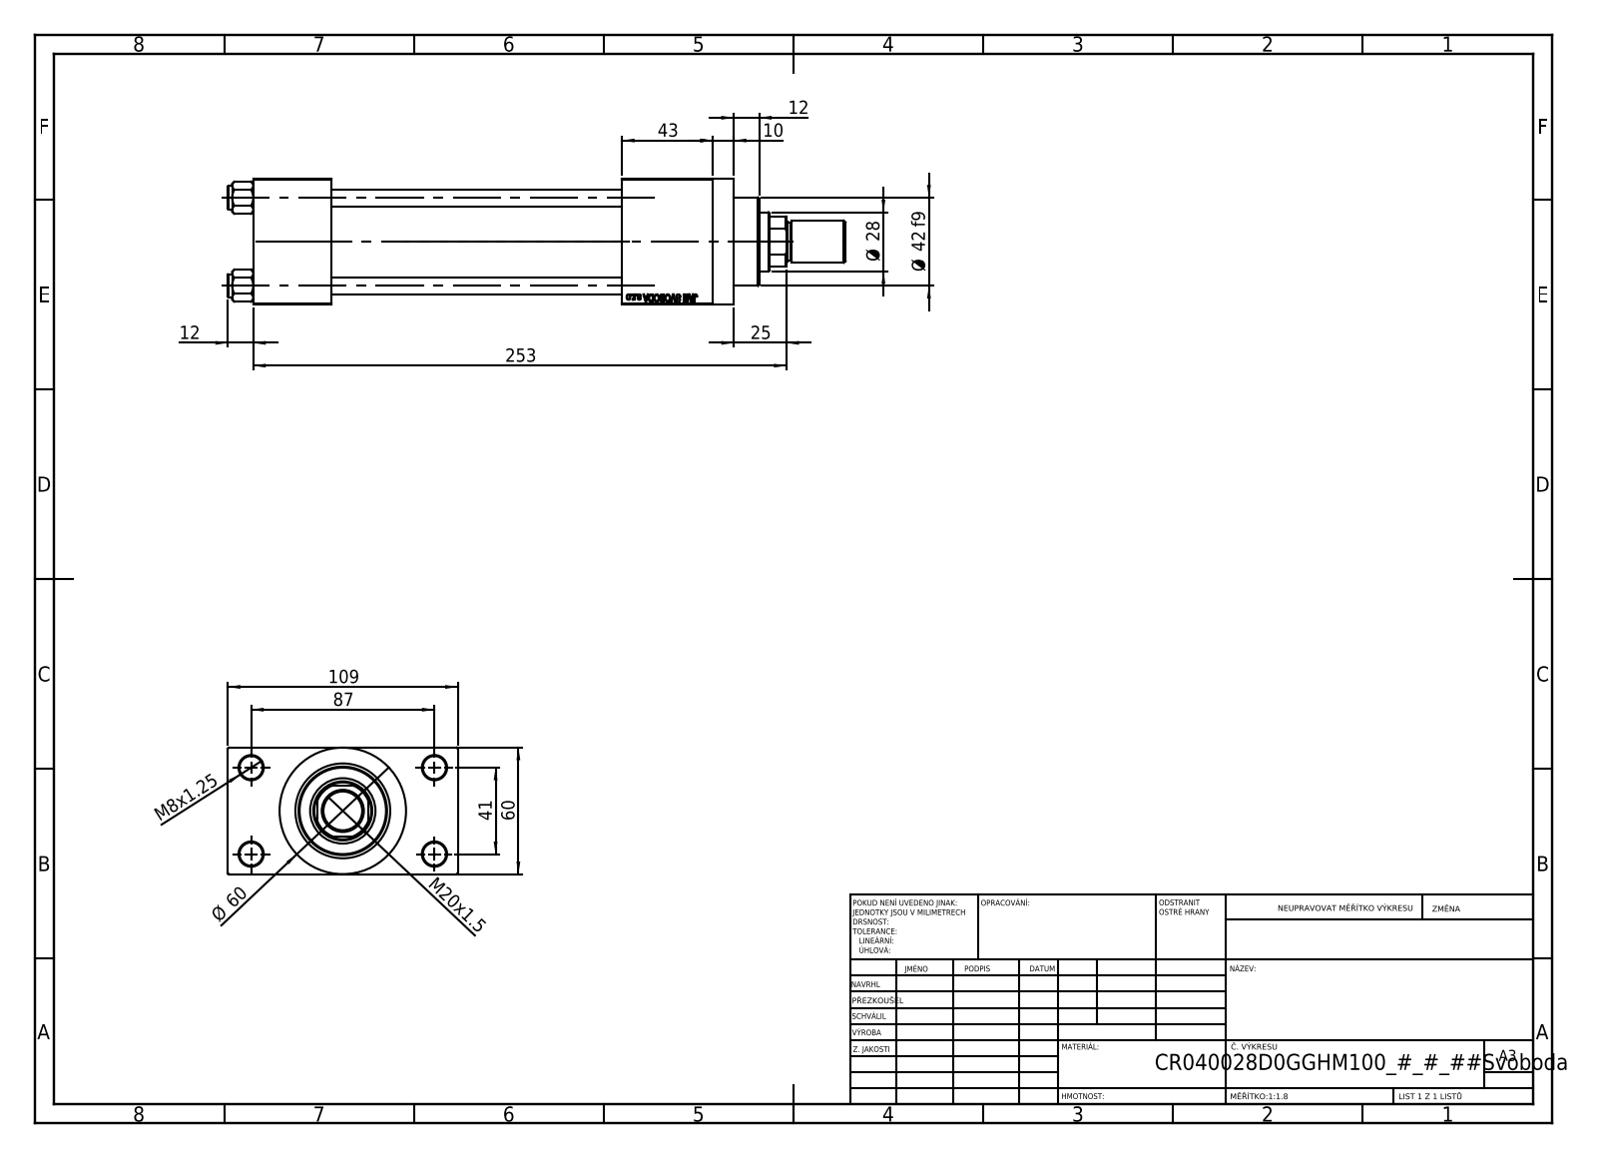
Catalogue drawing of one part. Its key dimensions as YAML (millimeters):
part_name: "V215_VC_A; V215CR_D_TYCINKA; V215CR_D_Body; V215CR_VCP_D (+2 more)"
step_written_by: "SolidWorks 2019 (CONFIG_CONTROL_DESIGN)"
units: millimeters
bodies: {solids: 12, faces: 1119, planar: 502, cylindrical: 93, other: 524}
overall_size: [293, 109, 60]
volume: 640540
surface_area: 166954
round_holes:
  - {diameter: 8, count: 4}
  - {diameter: 11, count: 4}
  - {diameter: 7, count: 2}
  - {diameter: 16.66, count: 2}
  - {diameter: 24, count: 2}
  - {diameter: 18.5, count: 1}
  - {diameter: 28, count: 1}
  - {diameter: 31, count: 1}
  - {diameter: 40, count: 1}
  - {diameter: 45, count: 1}
round_bosses_or_shafts:
  - {diameter: 11, count: 4}
  - {diameter: 60, count: 1}
  - {diameter: 46, count: 1}
  - {diameter: 42, count: 1}
  - {diameter: 20, count: 1}
  - {diameter: 18, count: 1}
partial_cylinders:
  - {radius: 13.5, count: 1}
face_to_face_distances: [60, 24.5, 84.5, 138, 37, 175, 218, 181, 43, 109]
hole_center_spacings: [22.65, 29.49, 41.7, 47.15, 48.09, 64.35, 76.49, 41]
